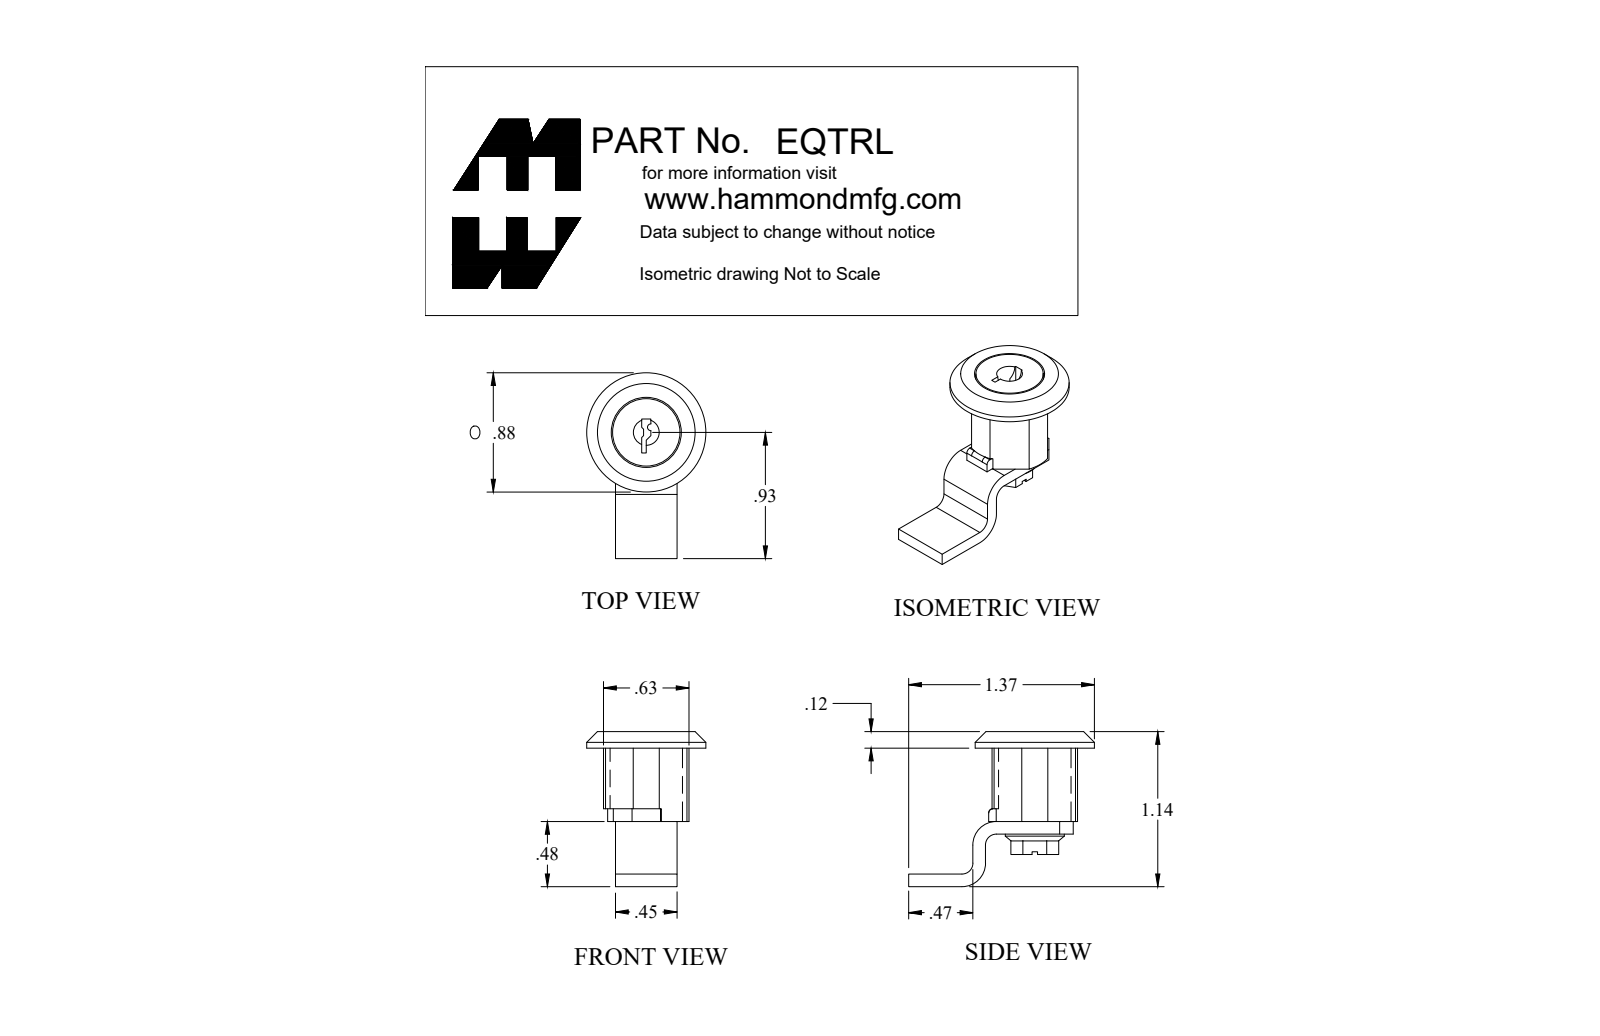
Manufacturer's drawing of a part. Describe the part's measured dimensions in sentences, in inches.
The part is named "EQTRL". Its 3-D file was written by "SolidWorks 2018 (AUTOMOTIVE_DESIGN)". It is 1 solid with 106 faces: 76 planar, 22 cylindrical and 8 other. Overall it measures 1.369 by 1.142 by 0.878 inches. Its volume is 0.241 cubic inches and its surface area 5.014 square inches. Round holes: 1 of diameter 0.516, 1 of diameter 0.535. Round bosses or shafts: 1 of diameter 0.878, 1 of diameter 0.496, 1 of diameter 0.435. Partial cylindrical surfaces (rounded edges, fillets, slot ends): 2 of radius 0.081, 2 of radius 0.174, 1 of radius 0.025, 1 of radius 0.03, 1 of radius 0.315. The main face-to-face distances are 0.122, 0.56, 0.093, 0.387, 0.54, 0.662, 0.206, 0.334, 0.456, 0.48.
